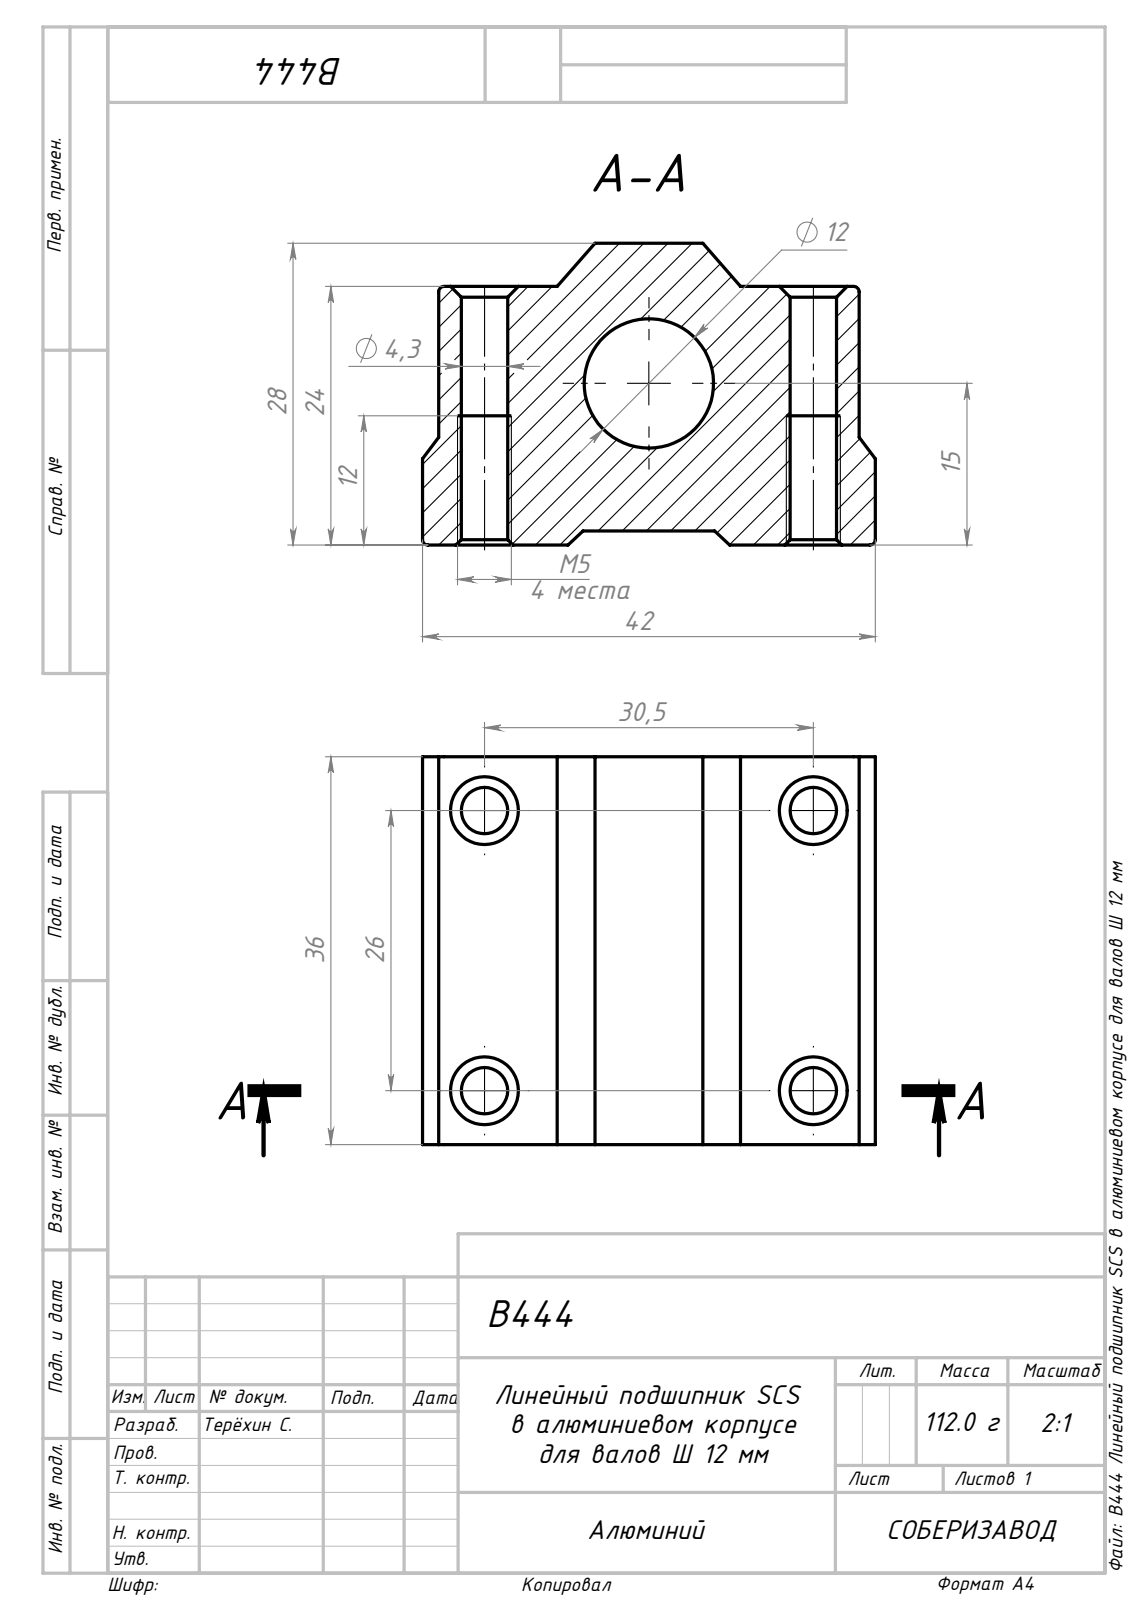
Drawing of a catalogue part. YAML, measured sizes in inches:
part_name: "Сборка2; B444 Линейный подшипник SCS в алюминиевом корпусе для валов Ø 12 мм_SCS12UU"
step_written_by: "SolidWorks 2024 (AUTOMOTIVE_DESIGN)"
units: inches
bodies: {solids: 1, faces: 48, planar: 18, cylindrical: 14, other: 16}
overall_size: [1.654, 1.417, 1.102]
volume: 1.859
surface_area: 14.08
round_holes:
  - {diameter: 0.169, count: 4}
  - {diameter: 0.472, count: 1}
partial_cylinders:
  - {radius: 0.02, count: 4}
face_to_face_distances: [1.417, 0.945, 0.059, 1.594, 1.535, 0.051, 0.894, 1.102, 1.051, 0.157]
hole_center_spacings: [1.024, 1.201, 1.578]
